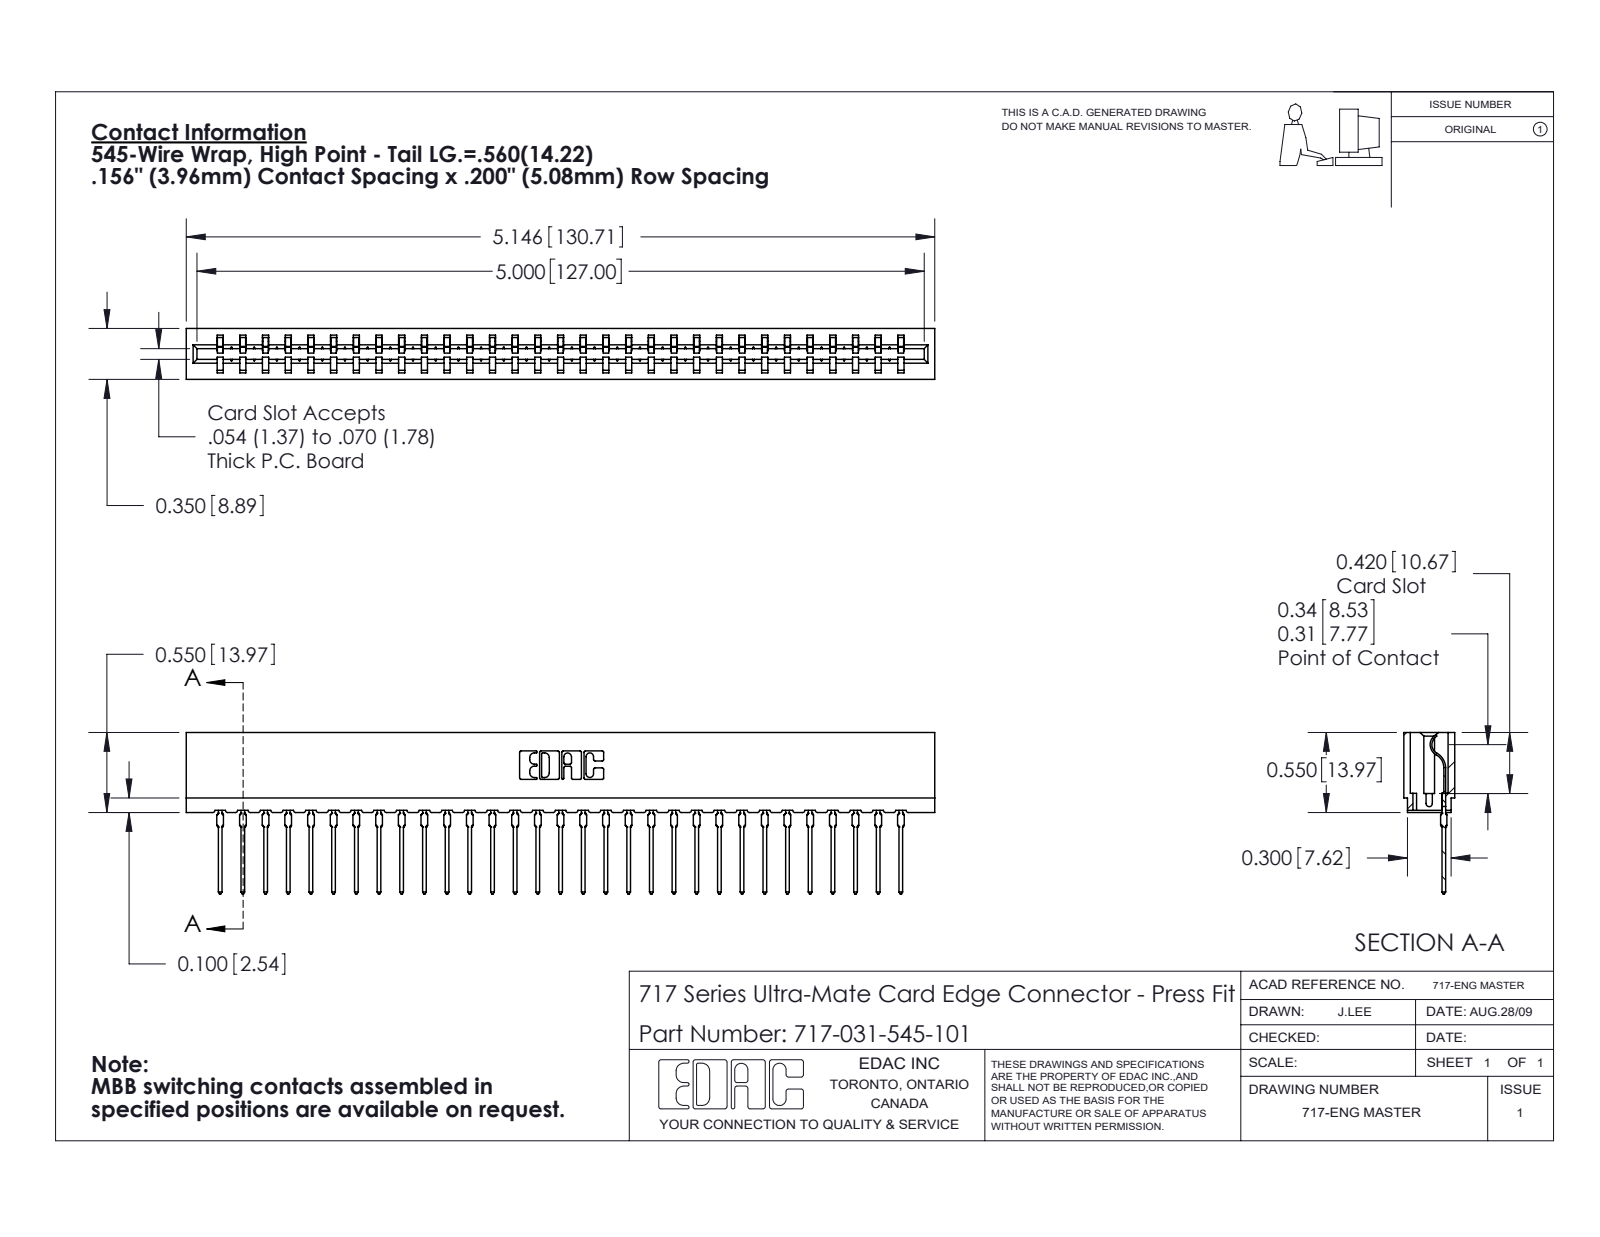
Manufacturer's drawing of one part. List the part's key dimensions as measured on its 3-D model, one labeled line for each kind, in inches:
Part name (STEP PRODUCT): 717 Part_Insulator Option - 06; 717-031-545-101; 745-292-001_545
STEP written by: SolidWorks 2020 (CONFIG_CONTROL_DESIGN)
Units: inches
Bodies: 32 solids, 3597 faces (2162 planar, 629 cylindrical, 806 other)
Overall size (bounding box): 5.146 × 1.109 × 0.35
Volume: 0.682 in³ · Surface area: 24.9 in²
Partial cylindrical surfaces — rounded edges, fillets, slot ends (radius × count): R0.015 ×62, R0.021 ×62, R0.01 ×22, R0.007 ×6, R0.031 ×6, R0.005 ×4, R0.011 ×4, R0.026 ×3
Main face-to-face distances: 0.212, 0.138, 0.35, 0.074, 0.063, 0.287, 0.076, 0.149, 0.045, 0.305
